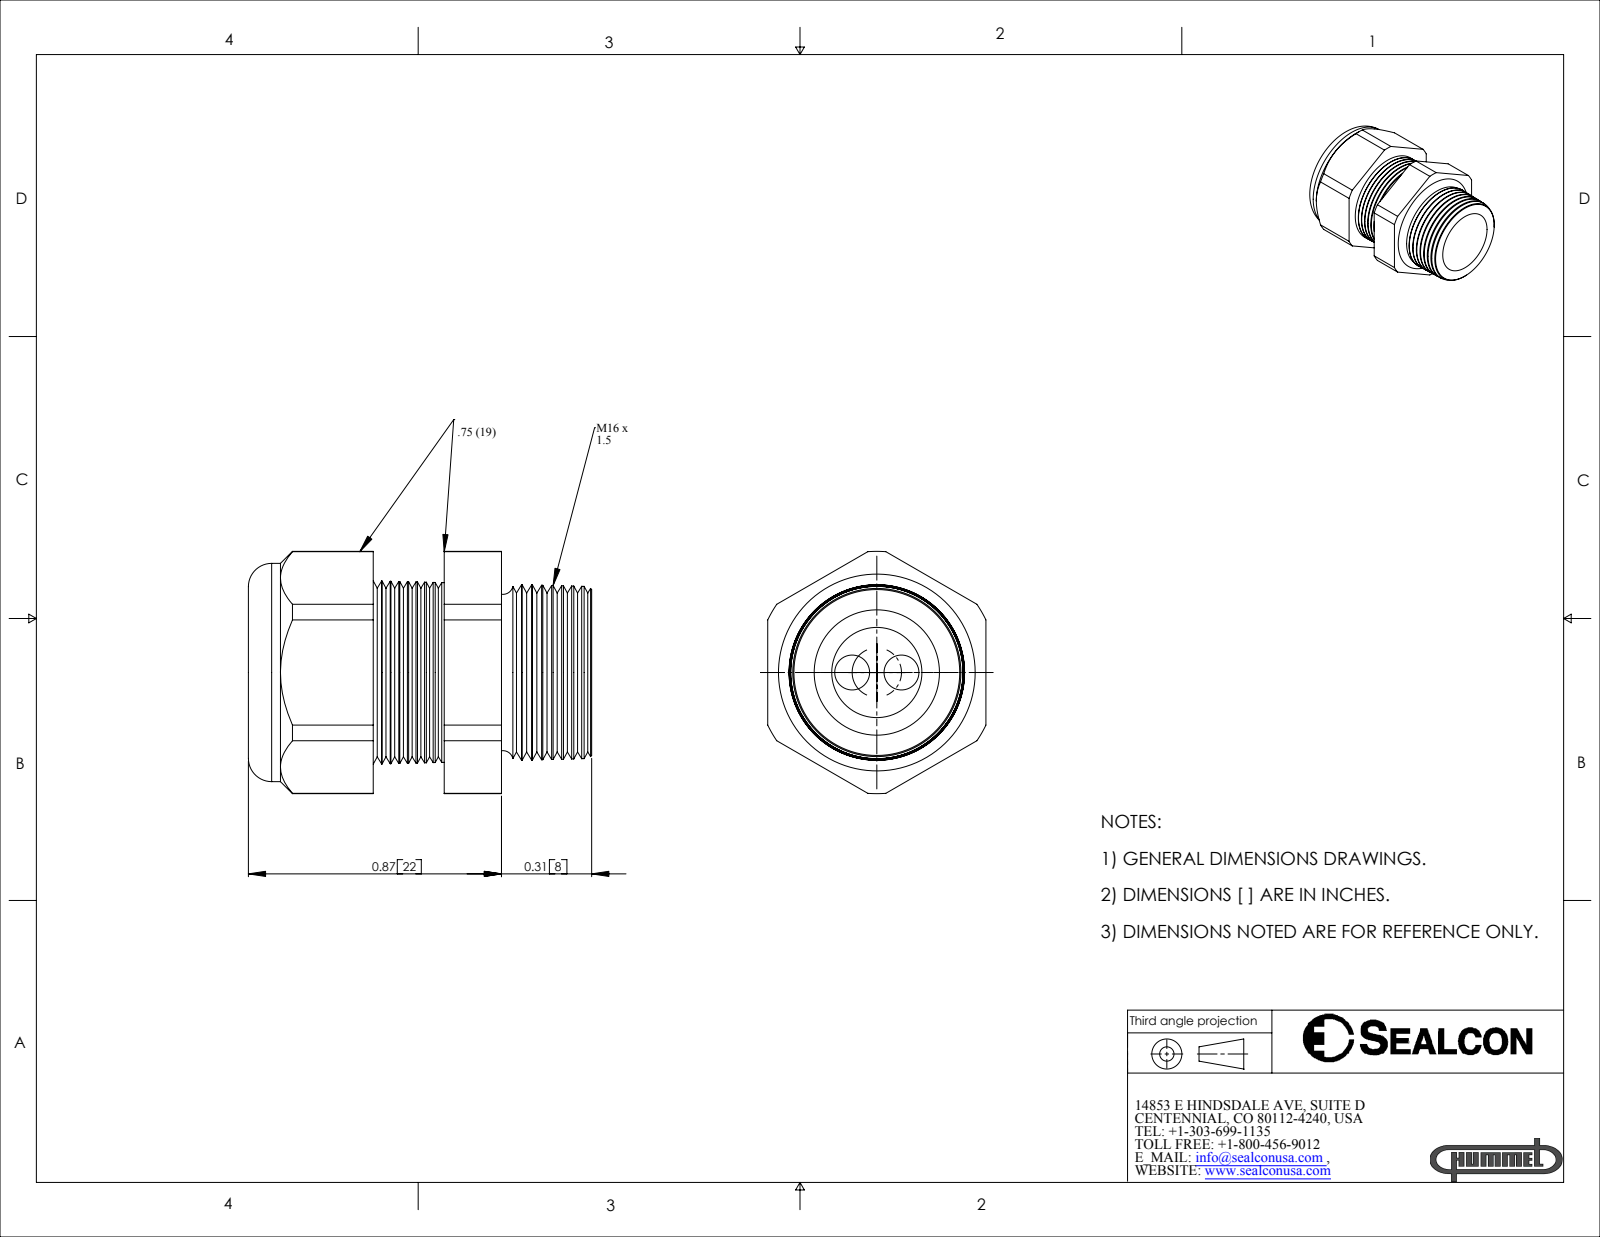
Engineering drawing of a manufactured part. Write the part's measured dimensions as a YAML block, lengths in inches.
part_name: "CD16M2-GY"
step_written_by: "SolidWorks 2007 (CONFIG_CONTROL_DESIGN)"
units: inches
bodies: {solids: 2, faces: 154, planar: 20, cylindrical: 24, other: 110}
overall_size: [1.18, 0.833, 0.75]
volume: 0.334
surface_area: 6.163
round_holes:
  - {diameter: 0.12, count: 2}
  - {diameter: 0.29, count: 1}
  - {diameter: 0.31, count: 1}
round_bosses_or_shafts:
  - {diameter: 0.75, count: 1}
partial_cylinders:
  - {radius: 0.416, count: 1}
face_to_face_distances: [0.75, 0.673, 0.75, 0.429, 0.244, 0.87, 0.441, 0.197, 1.18, 0.751]
hole_center_spacings: [0.085, 0.169]
